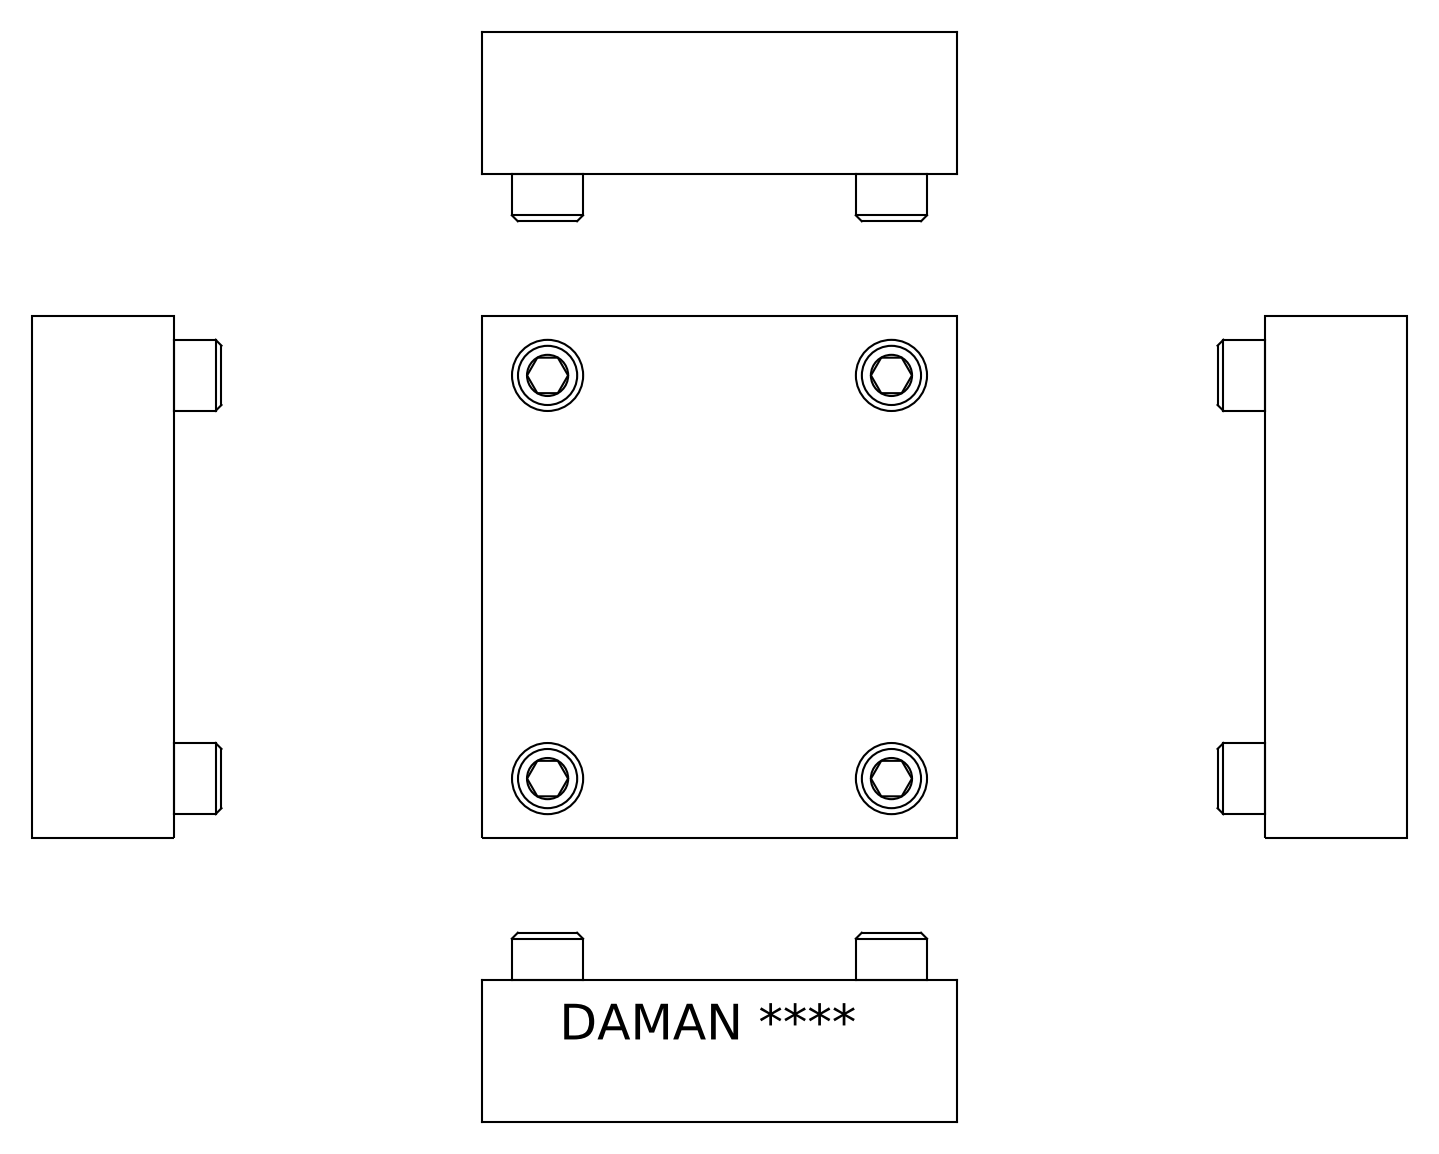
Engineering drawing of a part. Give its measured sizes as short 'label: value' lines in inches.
name: Part_DD05CPP_3D
written by: Autodesk Inventor 2020 (AUTOMOTIVE_DESIGN)
unit: in
bodies: 1 solid, 290 faces (208 planar, 9 cylindrical, 73 other)
size: 2.75 × 2.5 × 0.75
volume: 4.89 in³; area: 24.31 in²
holes: 5× ⌀0.625, 4× ⌀0.281
face distances: 0.75, 2.5, 2.75, 0.052, 0.698, 2.748, 0.143, 0.025, 0.024, 0.409
hole spacings: 1.171, 1.287, 2.793, 0.546, 0.546, 0.688, 0.689, 0.719
